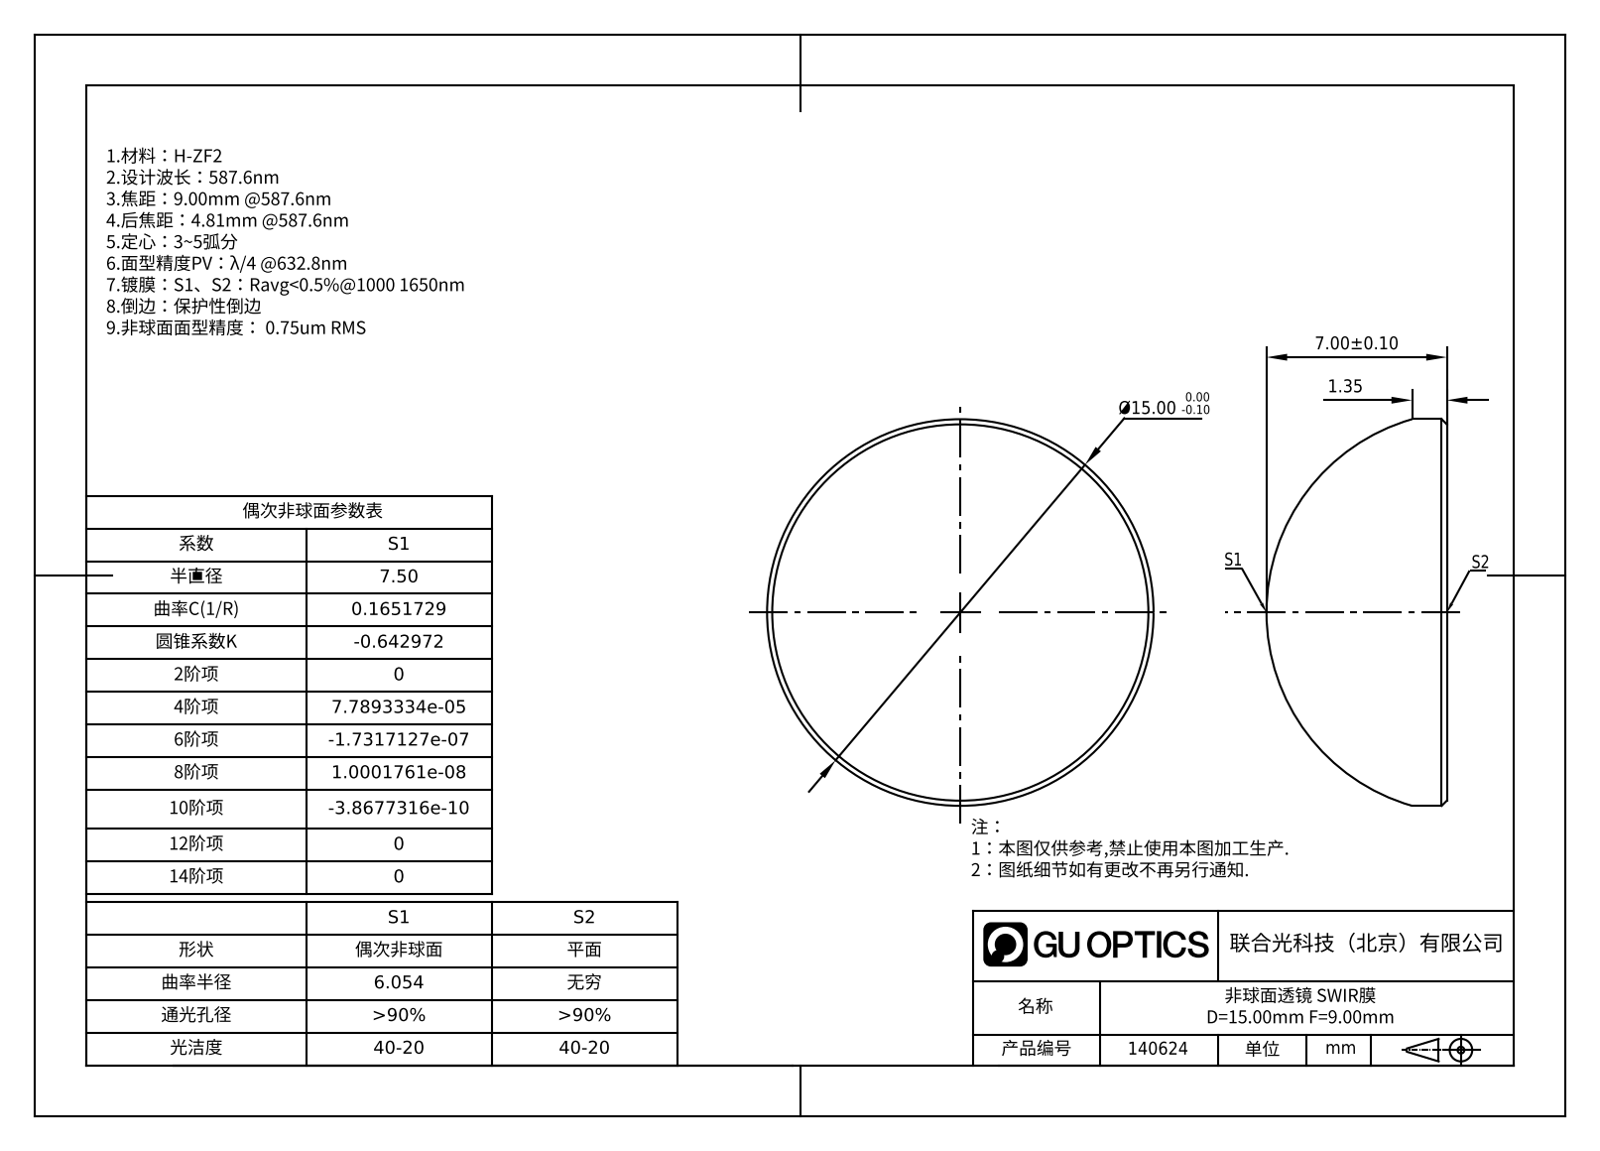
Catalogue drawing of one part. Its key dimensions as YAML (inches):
part_name: "GLA11-015-9-SWIR"
step_written_by: "SolidWorks 2022 (AUTOMOTIVE_DESIGN)"
units: inches
bodies: {solids: 1, faces: 7, planar: 1, cylindrical: 2, other: 4}
overall_size: [0.591, 0.591, 0.276]
volume: 0.051
surface_area: 0.794
round_bosses_or_shafts:
  - {diameter: 0.591, count: 1}
